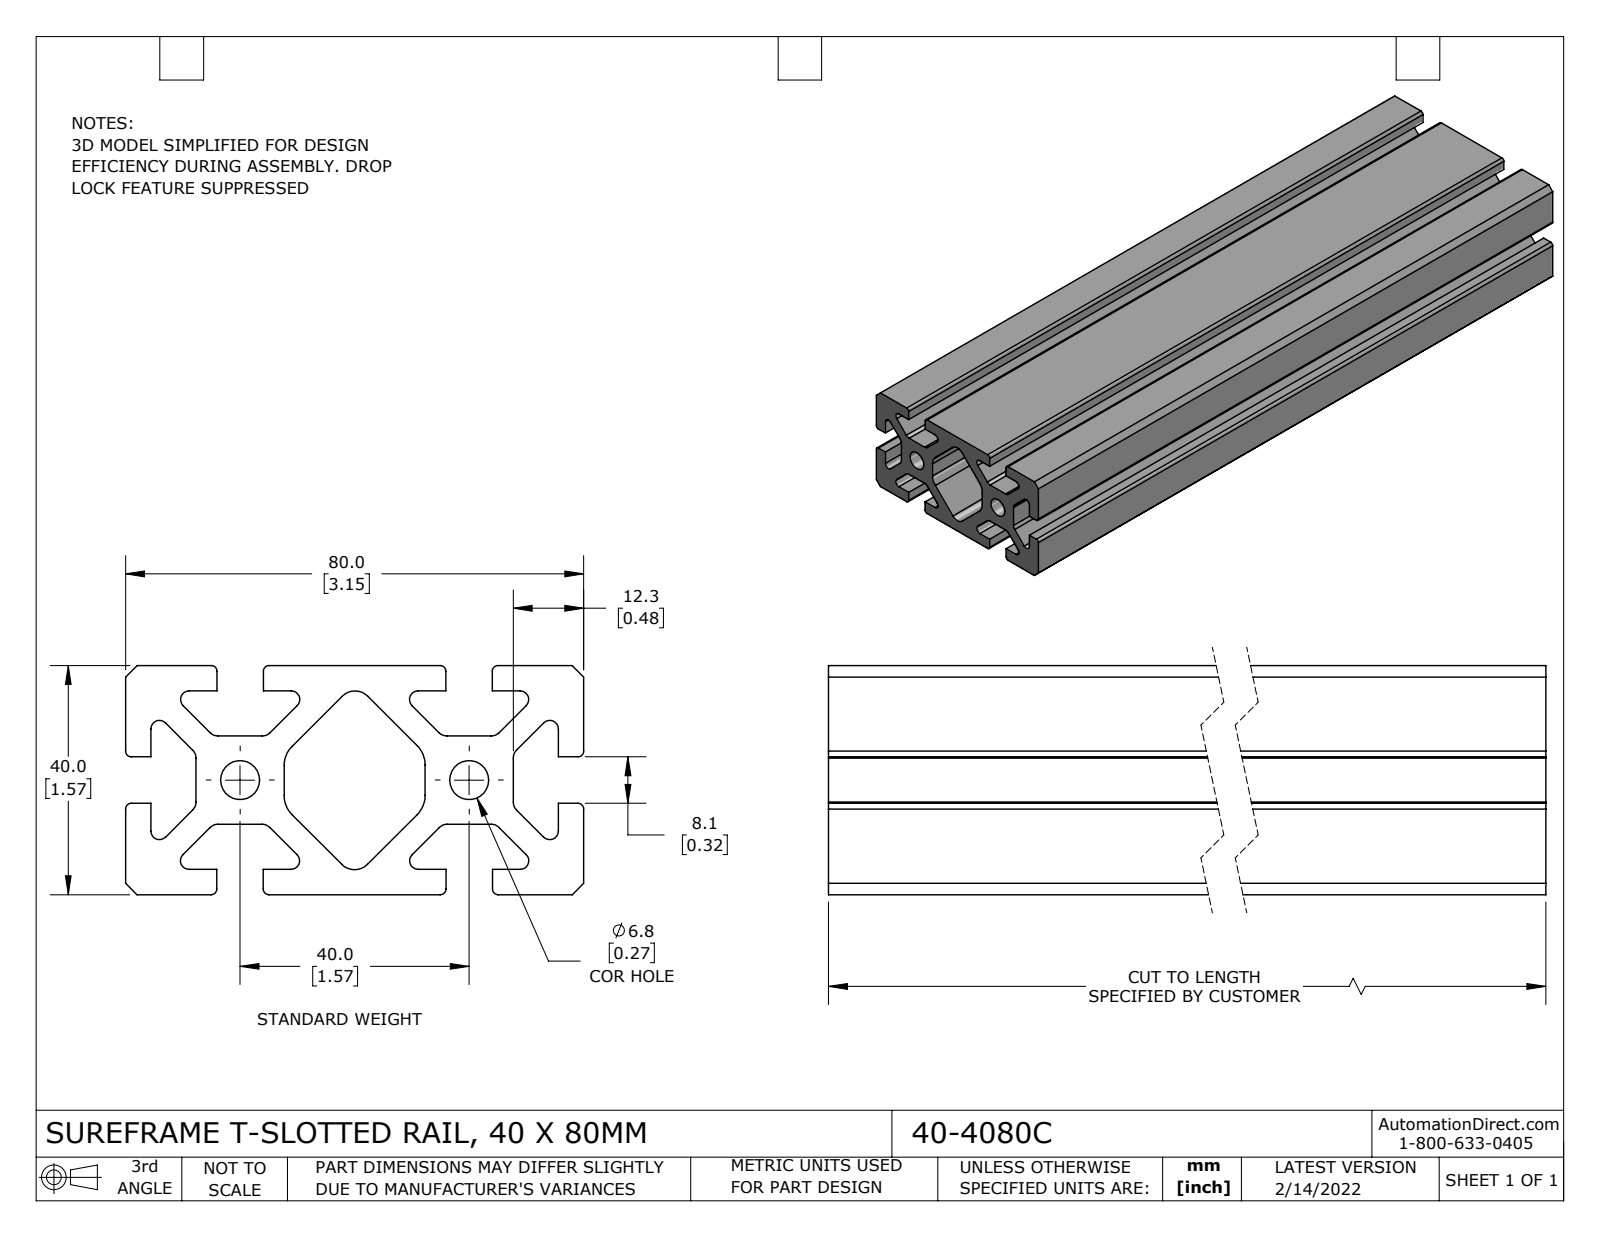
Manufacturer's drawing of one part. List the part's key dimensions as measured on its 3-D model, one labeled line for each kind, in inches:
Part name (STEP PRODUCT): 40-4080C
STEP written by: SolidWorks 2021 (CONFIG_CONTROL_DESIGN)
Units: inches
Bodies: 1 solid, 116 faces (64 planar, 52 cylindrical, 0 other)
Overall size (bounding box): 10 × 3.15 × 1.575
Volume: 24.81 in³ · Surface area: 244.1 in²
Round holes (diameter × count): ⌀0.268 ×2
Partial cylindrical surfaces — rounded edges, fillets, slot ends (radius × count): R0.039 ×12, R0.059 ×12, R0.079 ×12, R0.187 ×4, R0.125 ×2
Main face-to-face distances: 1.575, 0.174, 0.484, 0.31, 1.401, 0.169, 1.113, 1.091, 0.917, 1.113
Hole centre spacings: 1.575
